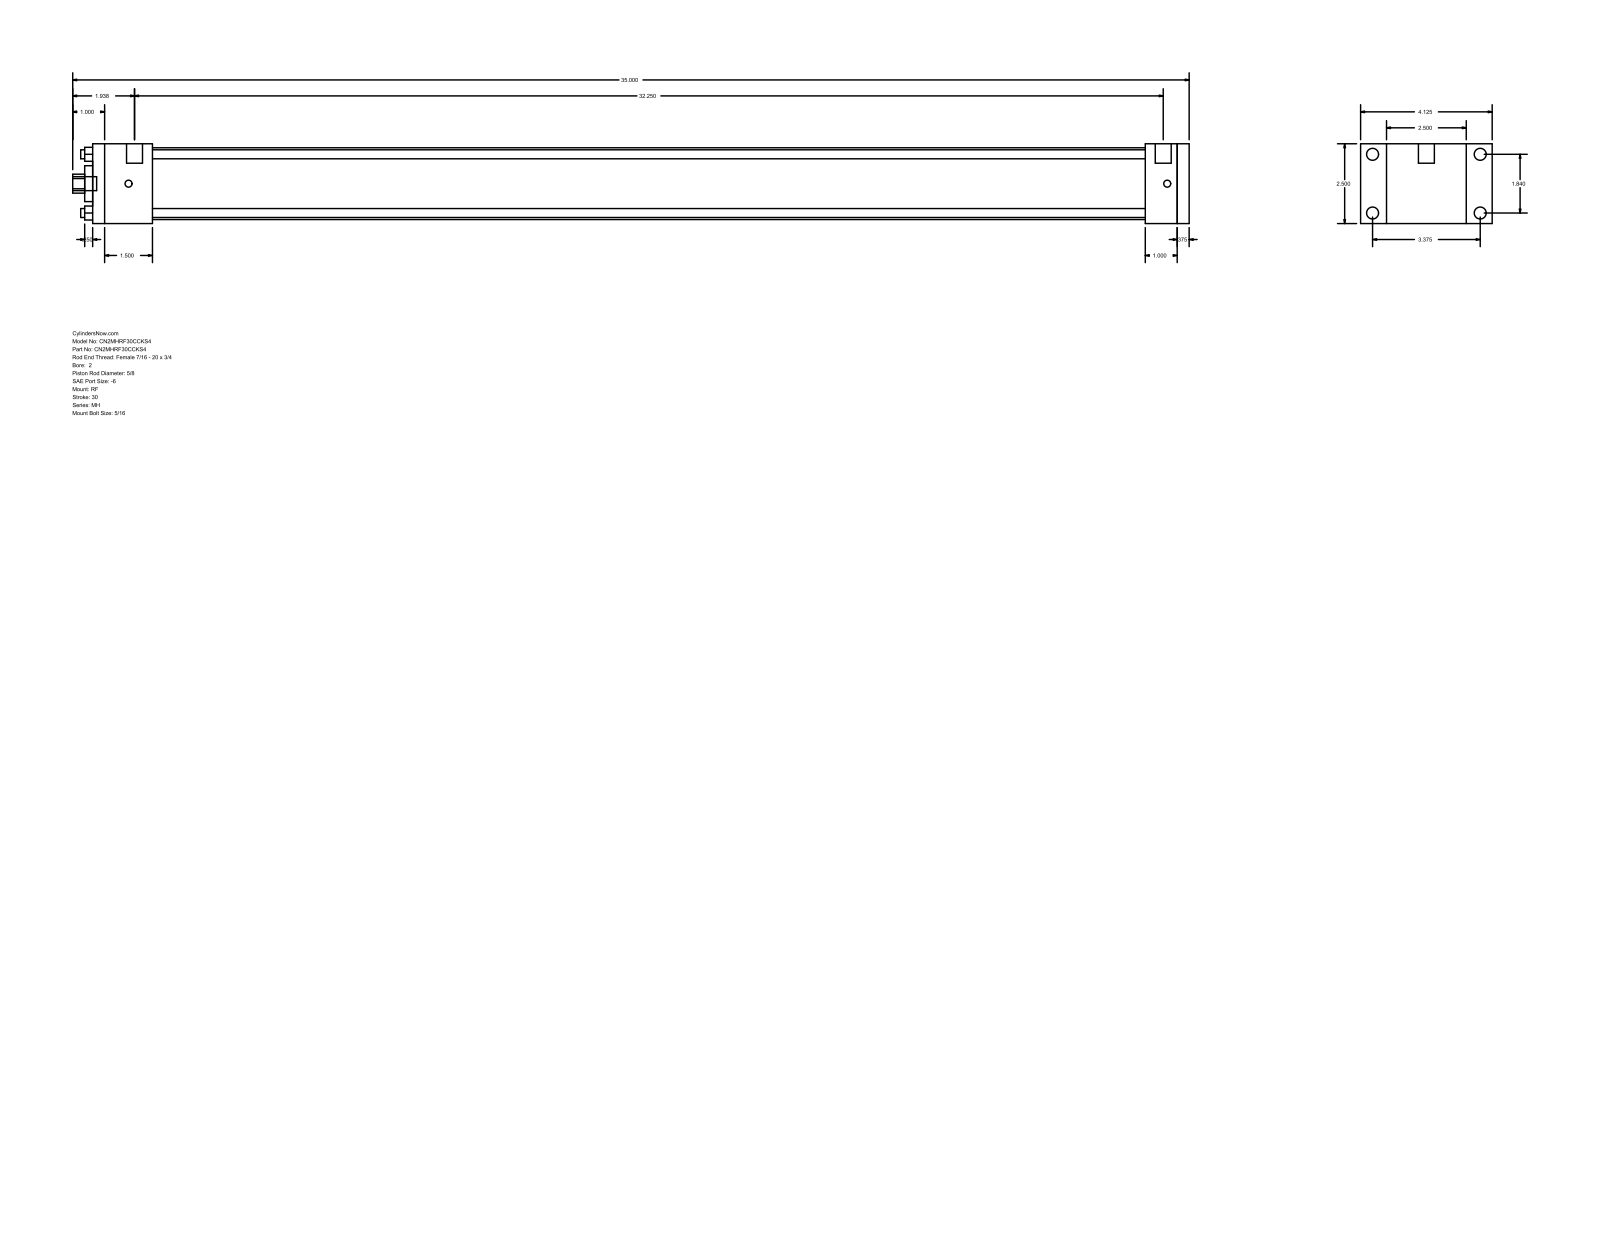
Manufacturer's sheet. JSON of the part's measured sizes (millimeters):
{"part_name": "MH_RF__0200_0.625", "step_written_by": "GSSL Pune (CONFIG_CONTROL_DESIGN)", "units": "millimeters", "bodies": {"solids": 0, "faces": 92, "planar": 64, "cylindrical": 28, "other": 0}, "overall_size": [889, 104.78, 63.5], "round_holes": [[7.14, 4], [15.88, 1], [28.57, 1], [57.15, 1]], "round_bosses_or_shafts": [[9.53, 4], [5.56, 4], [12.7, 2], [11.11, 1]], "partial_cylinders_radius": [[7.54, 1]], "face_to_face_distances": [63.5, 873.12, 9.52, 863.6, 25.4, 47.62, 838.2, 790.58, 815.98, 825.5], "hole_center_spacings": [33.05, 46.74, 66.1]}
